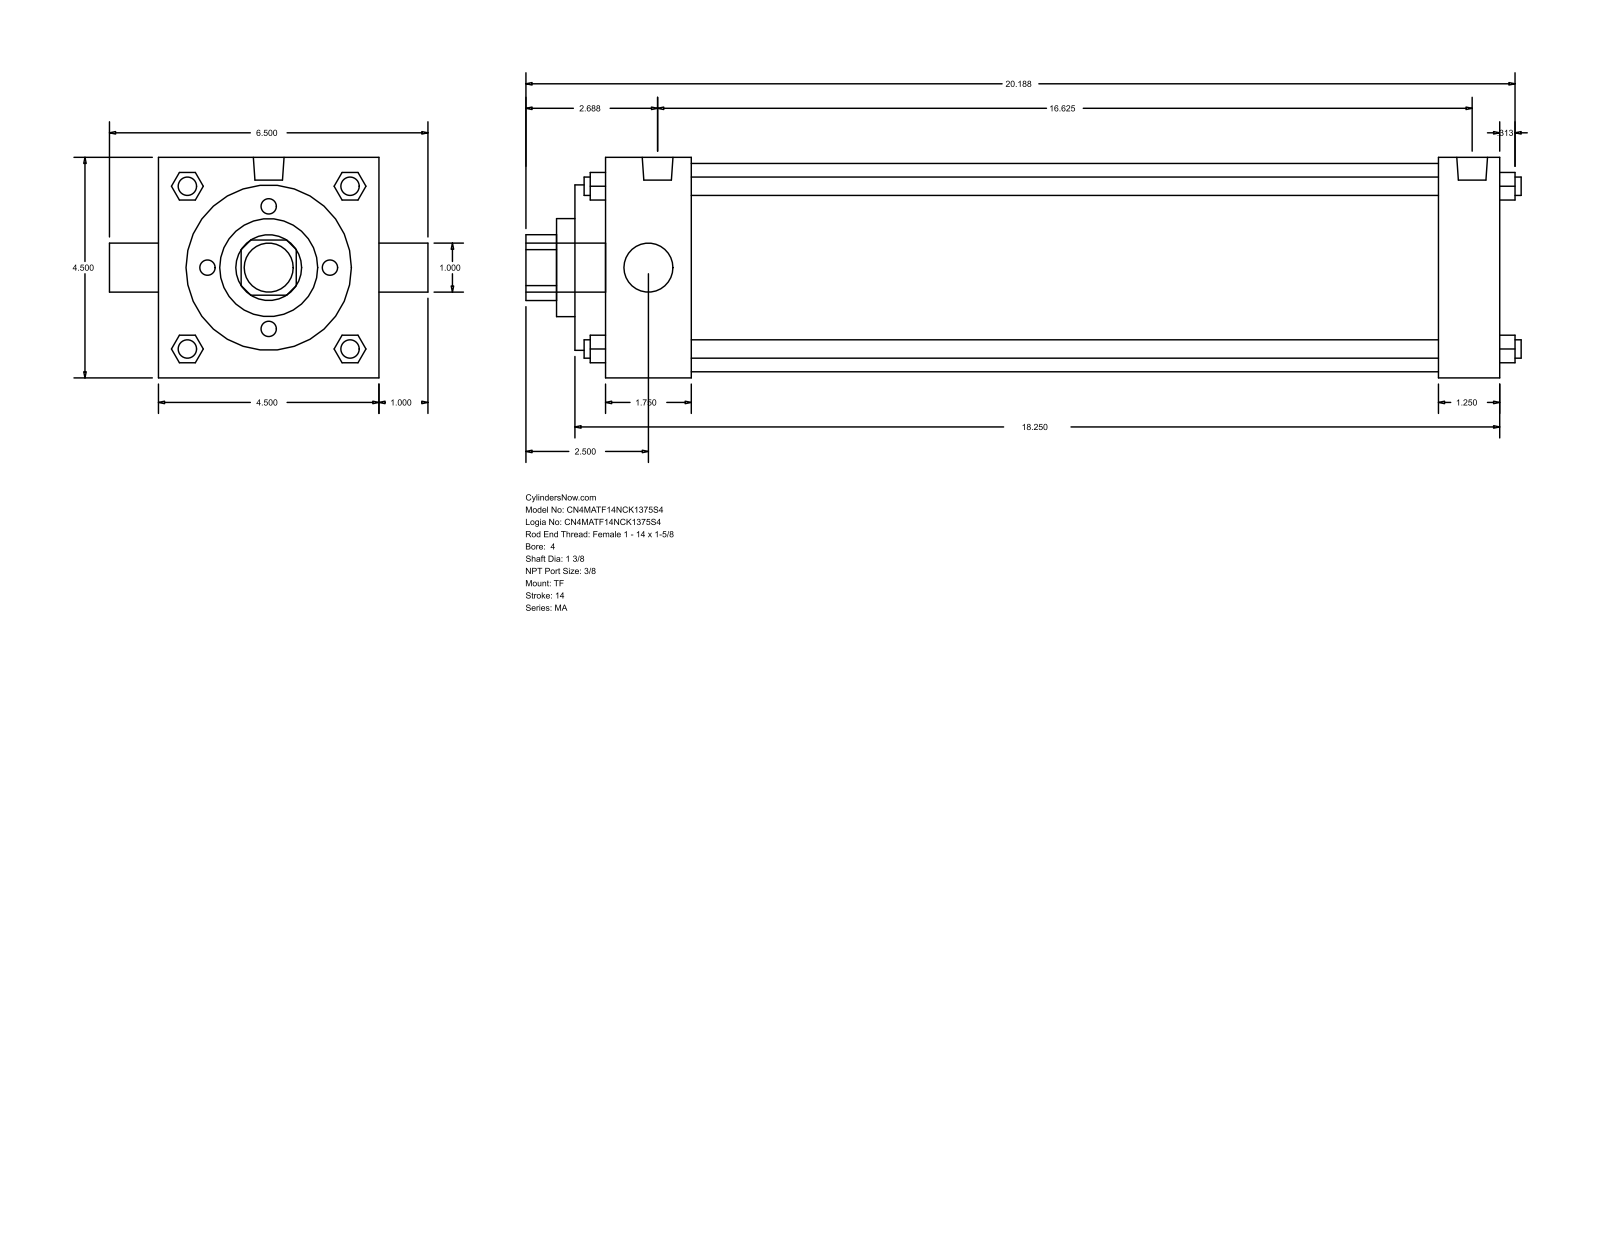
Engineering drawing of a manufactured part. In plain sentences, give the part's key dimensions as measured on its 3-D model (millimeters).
The part is named "MA_TF__0400_1.375". Its 3-D file was written by "GSSL Pune (CONFIG_CONTROL_DESIGN)". It is 0 solids with 122 faces: 93 planar, 29 cylindrical and 0 other. Overall it measures 515.94 by 165.1 by 114.3 millimeters. Round holes: 1 of diameter 25.4, 1 of diameter 34.92, 1 of diameter 50.8, 1 of diameter 85.72, 1 of diameter 107.95. Round bosses or shafts: 4 of diameter 9.53, 3 of diameter 11.11, 2 of diameter 15.93, 1 of diameter 25.4. Partial cylindrical surfaces (rounded edges, fillets, slot ends): 1 of radius 17.06. The main face-to-face distances are 114.3, 463.55, 479.42, 15.87, 447.67, 431.8, 31.75, 60.32, 44.45, 387.35.
